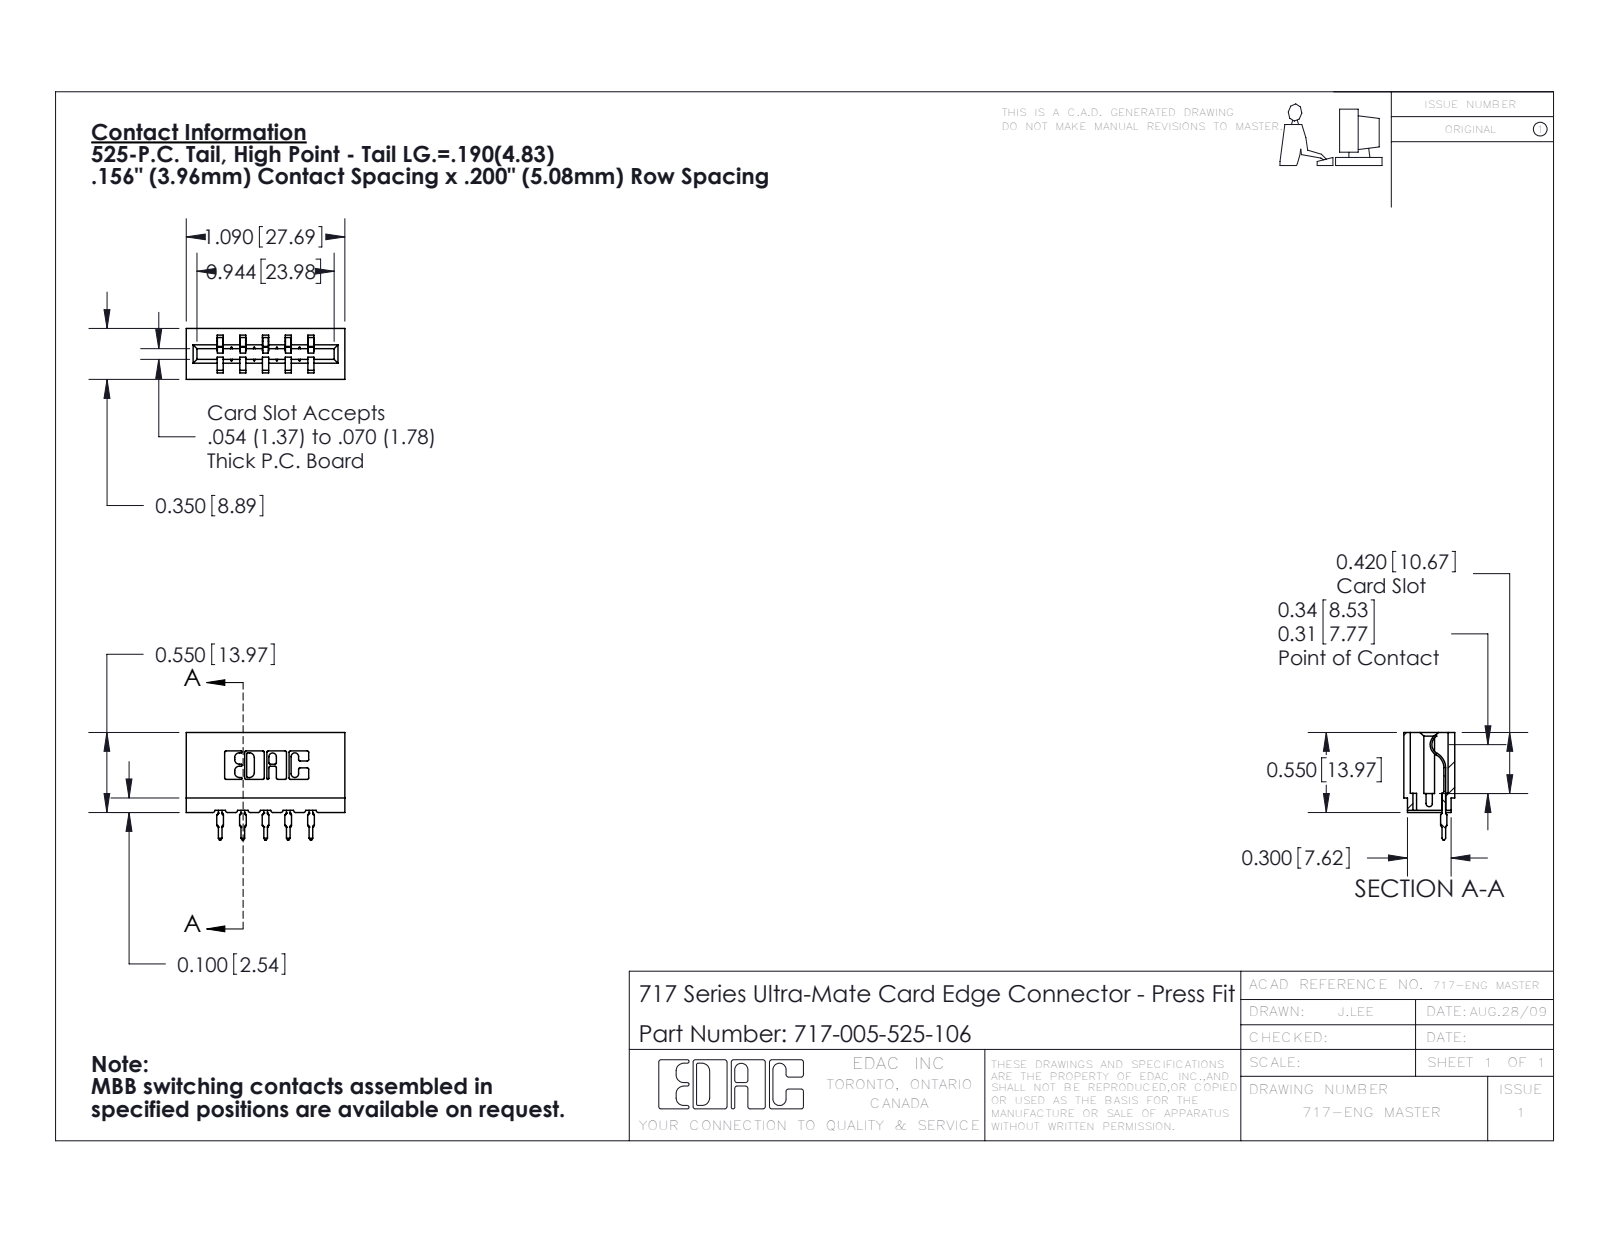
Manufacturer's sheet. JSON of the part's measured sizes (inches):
{"part_name": "717-005-525-106; 717 Part_Insulator Option - 06; 745-292-001_525", "step_written_by": "SolidWorks 2016 (CONFIG_CONTROL_DESIGN)", "units": "inches", "bodies": {"solids": 6, "faces": 659, "planar": 394, "cylindrical": 135, "other": 130}, "overall_size": [1.09, 0.739, 0.35], "volume_in3": 0.153, "surface_area_in2": 4.8, "partial_cylinders_radius": [[0.01, 22], [0.015, 10], [0.021, 10], [0.007, 6], [0.031, 6], [0.005, 4], [0.011, 4], [0.026, 3]], "face_to_face_distances": [0.212, 0.156, 0.138, 0.35, 0.198, 0.042, 0.312, 0.468, 0.312, 0.074]}
